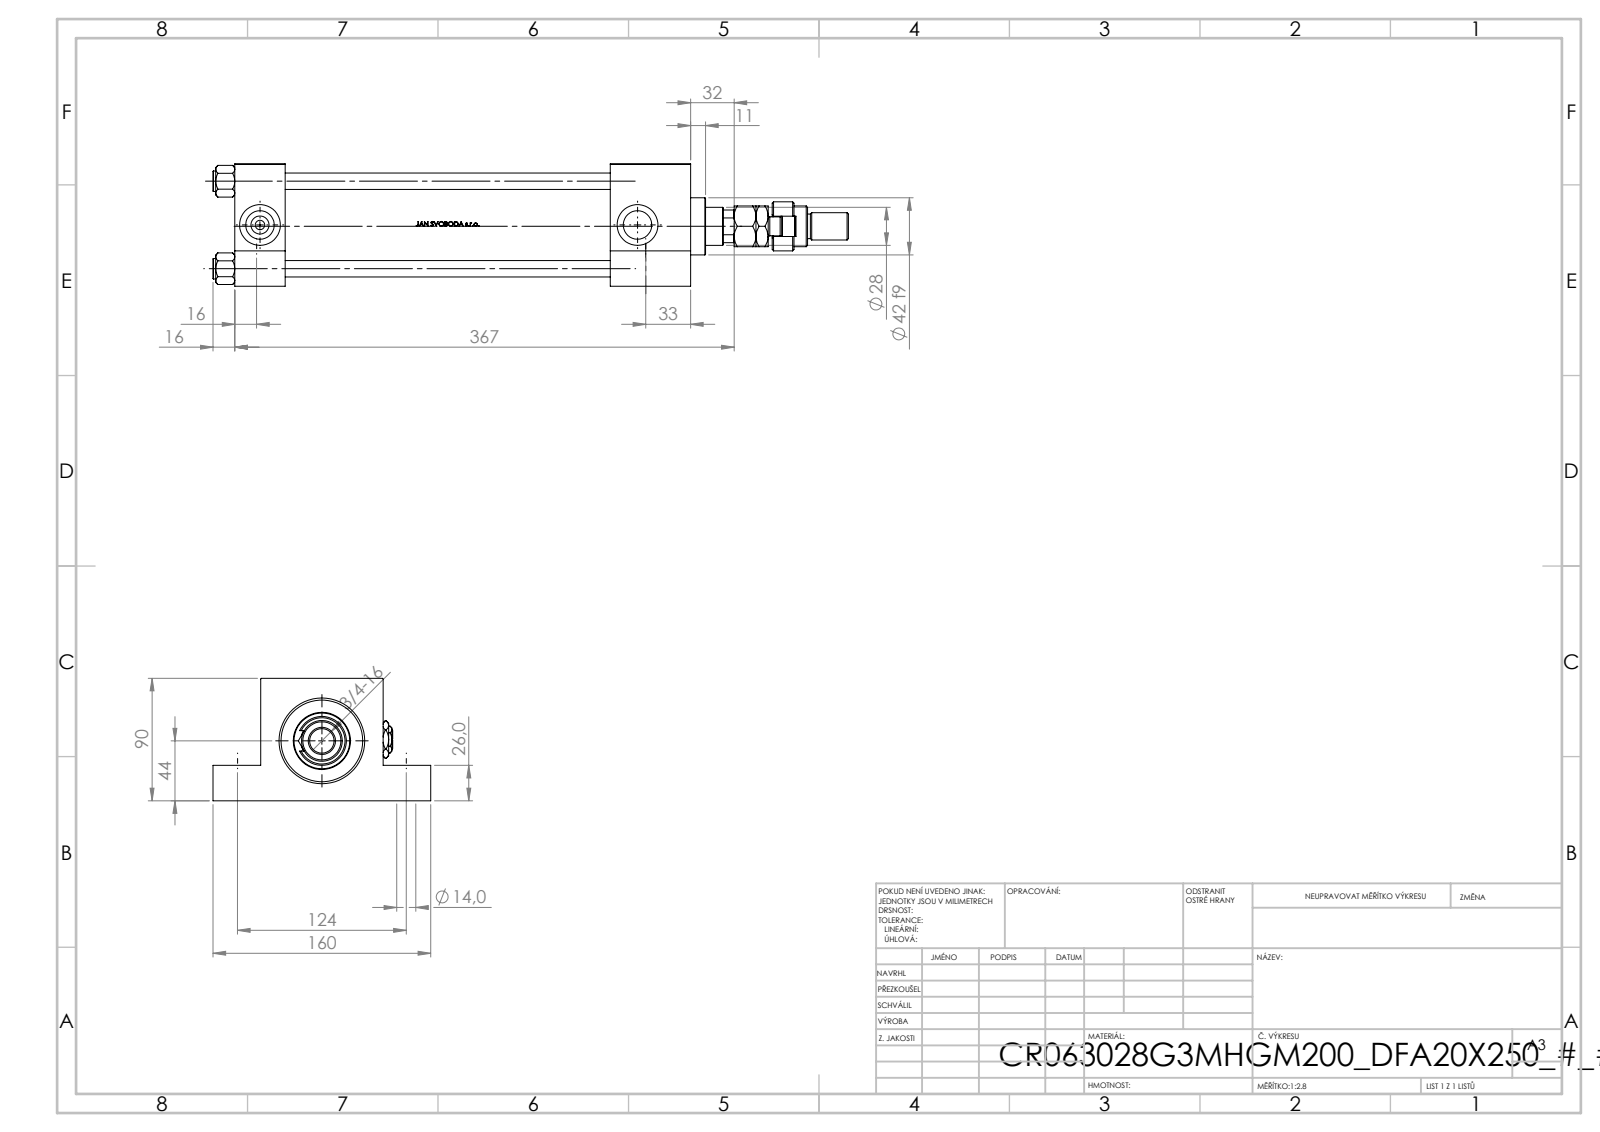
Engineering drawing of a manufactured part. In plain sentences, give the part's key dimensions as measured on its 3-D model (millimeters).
The part is named "V215CR_G_Body; V215_VC_A; V215CR_VCP_G; V215CR_G_TYCINKA (+4 more)". Its 3-D file was written by "SolidWorks 2019 (CONFIG_CONTROL_DESIGN)". It is 15 solids with 1269 faces: 506 planar, 145 cylindrical and 618 other. Overall it measures 467 by 160 by 90 millimeters. Its volume is 1 463 000 cubic millimeters and its surface area 335 190 square millimeters. Round holes: 4 of diameter 12, 4 of diameter 14, 2 of diameter 7, 2 of diameter 20.96, 2 of diameter 30, 1 of diameter 18.5, 1 of diameter 28, 1 of diameter 31, 1 of diameter 50, 1 of diameter 60, 1 of diameter 63. Round bosses or shafts: 4 of diameter 15, 1 of diameter 69, 1 of diameter 42, 1 of diameter 36, 1 of diameter 30, 1 of diameter 22, 1 of diameter 20, 1 of diameter 18. Partial cylindrical surfaces (rounded edges, fillets, slot ends): 1 of radius 7.5, 1 of radius 12, 1 of radius 13.5. The main face-to-face distances are 90, 37, 335, 298, 59, 276, 239, 26, 64, 35. The hole center spacings are 64.3, 44.77, 46.18, 90.93, 124, 286, 311.72, 277.5.
